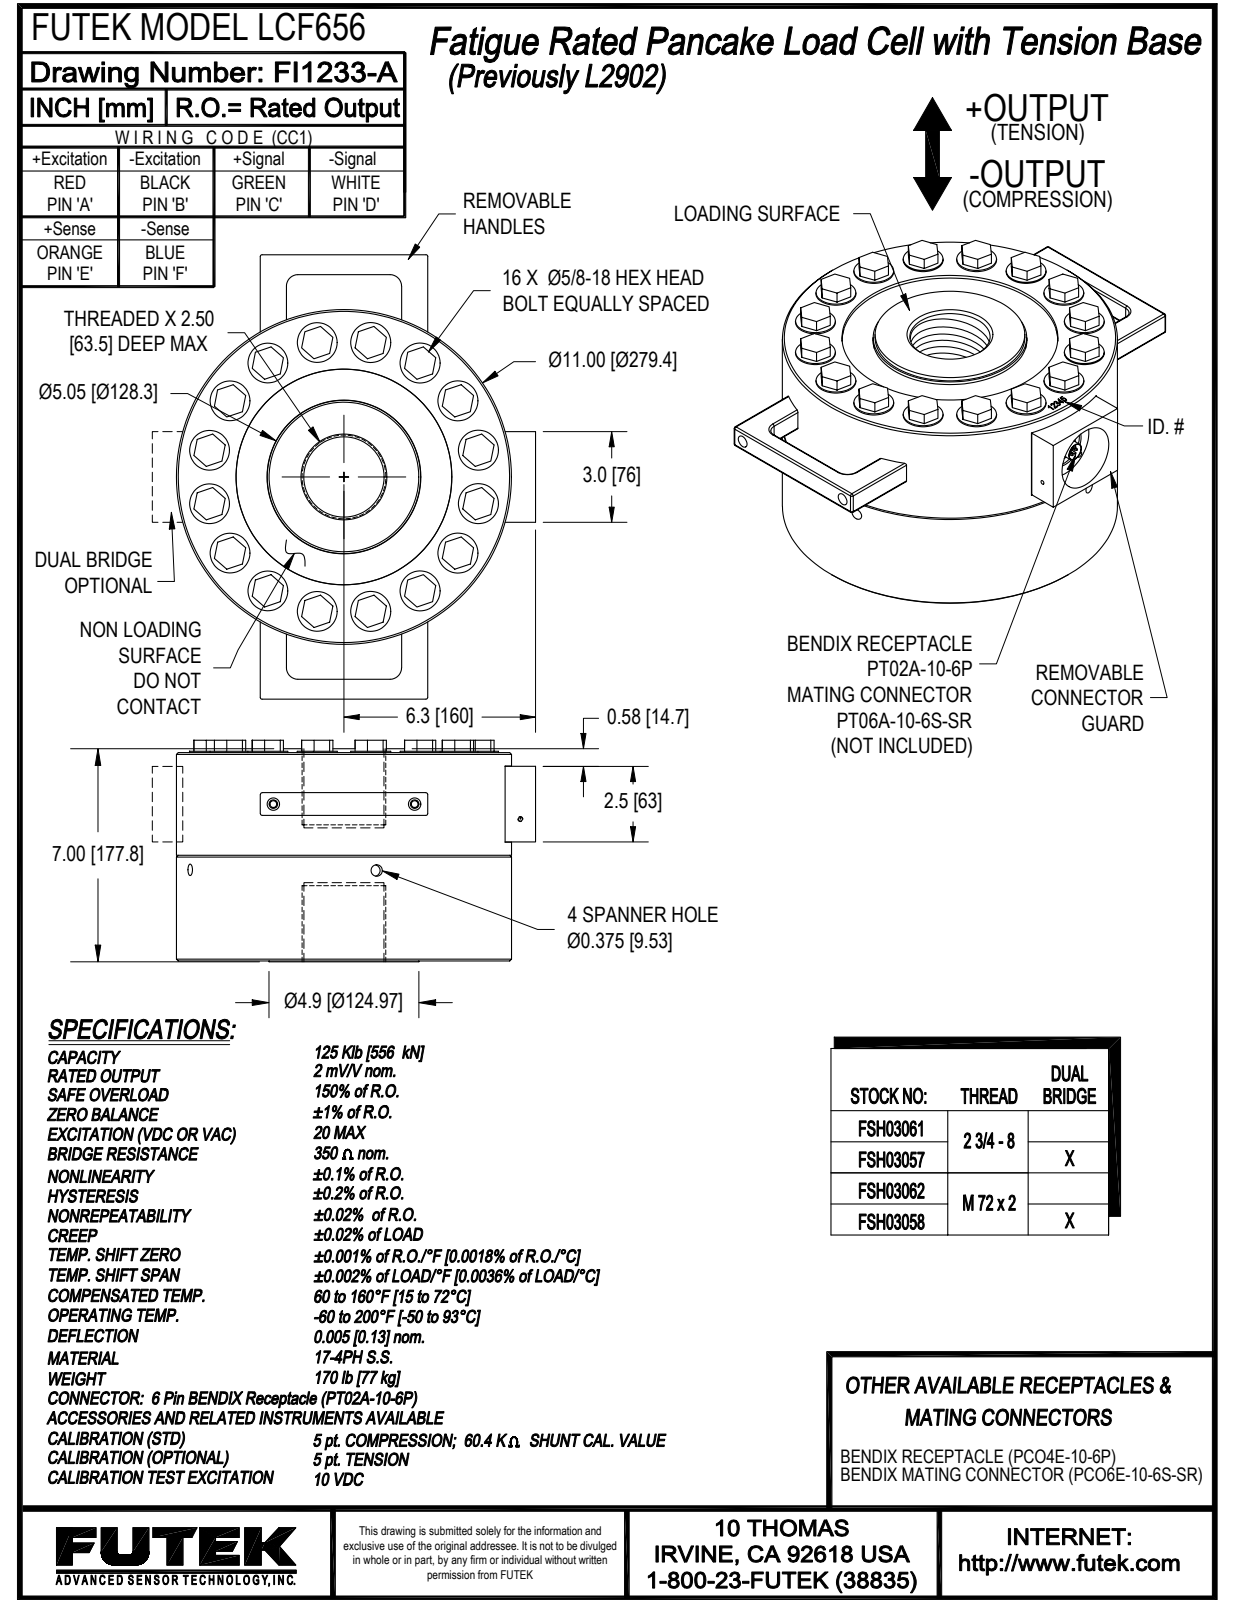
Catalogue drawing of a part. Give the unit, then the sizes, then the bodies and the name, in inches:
Units: inches
Overall size (bounding box): 14.502 × 11.881 × 7.234
Round holes (diameter × count): ⌀0.578 ×16, ⌀0.656 ×16, ⌀0.094 ×4, ⌀0.13 ×4, ⌀0.164 ×4, ⌀0.205 ×4, ⌀0.22 ×4, ⌀0.282 ×4, ⌀0.375 ×4, ⌀0.41 ×4, ⌀0.06 ×1, ⌀0.125 ×1
Round bosses / shafts (diameter × count): ⌀0.625 ×16, ⌀0.07 ×6, ⌀0.06 ×6, ⌀0.375 ×4, ⌀0.312 ×4, ⌀0.25 ×4, ⌀0.19 ×4, ⌀0.183 ×4
Partial cylindrical surfaces — rounded edges, fillets, slot ends (radius × count): R0.063 ×28, R0.05 ×4, R0.375 ×4, R5.5 ×2
Main face-to-face distances: 3.42, 0.05, 3.52, 6.84, 3.32, 0.105, 3.265, 0.1, 3.47, 3.37
Hole centre spacings: 8.315, 1.756, 3.444, 4.5, 8.827, 0.919, 1.3, 5
Volume: 620.6 in³ · Surface area: 971.3 in²
Bodies: 1 solid, 626 faces (337 planar, 192 cylindrical, 97 other)
Part name (STEP PRODUCT): LCF655; ~~PART1
STEP written by: Autodesk Inventor 2008 (AUTOMOTIVE_DESIGN)
